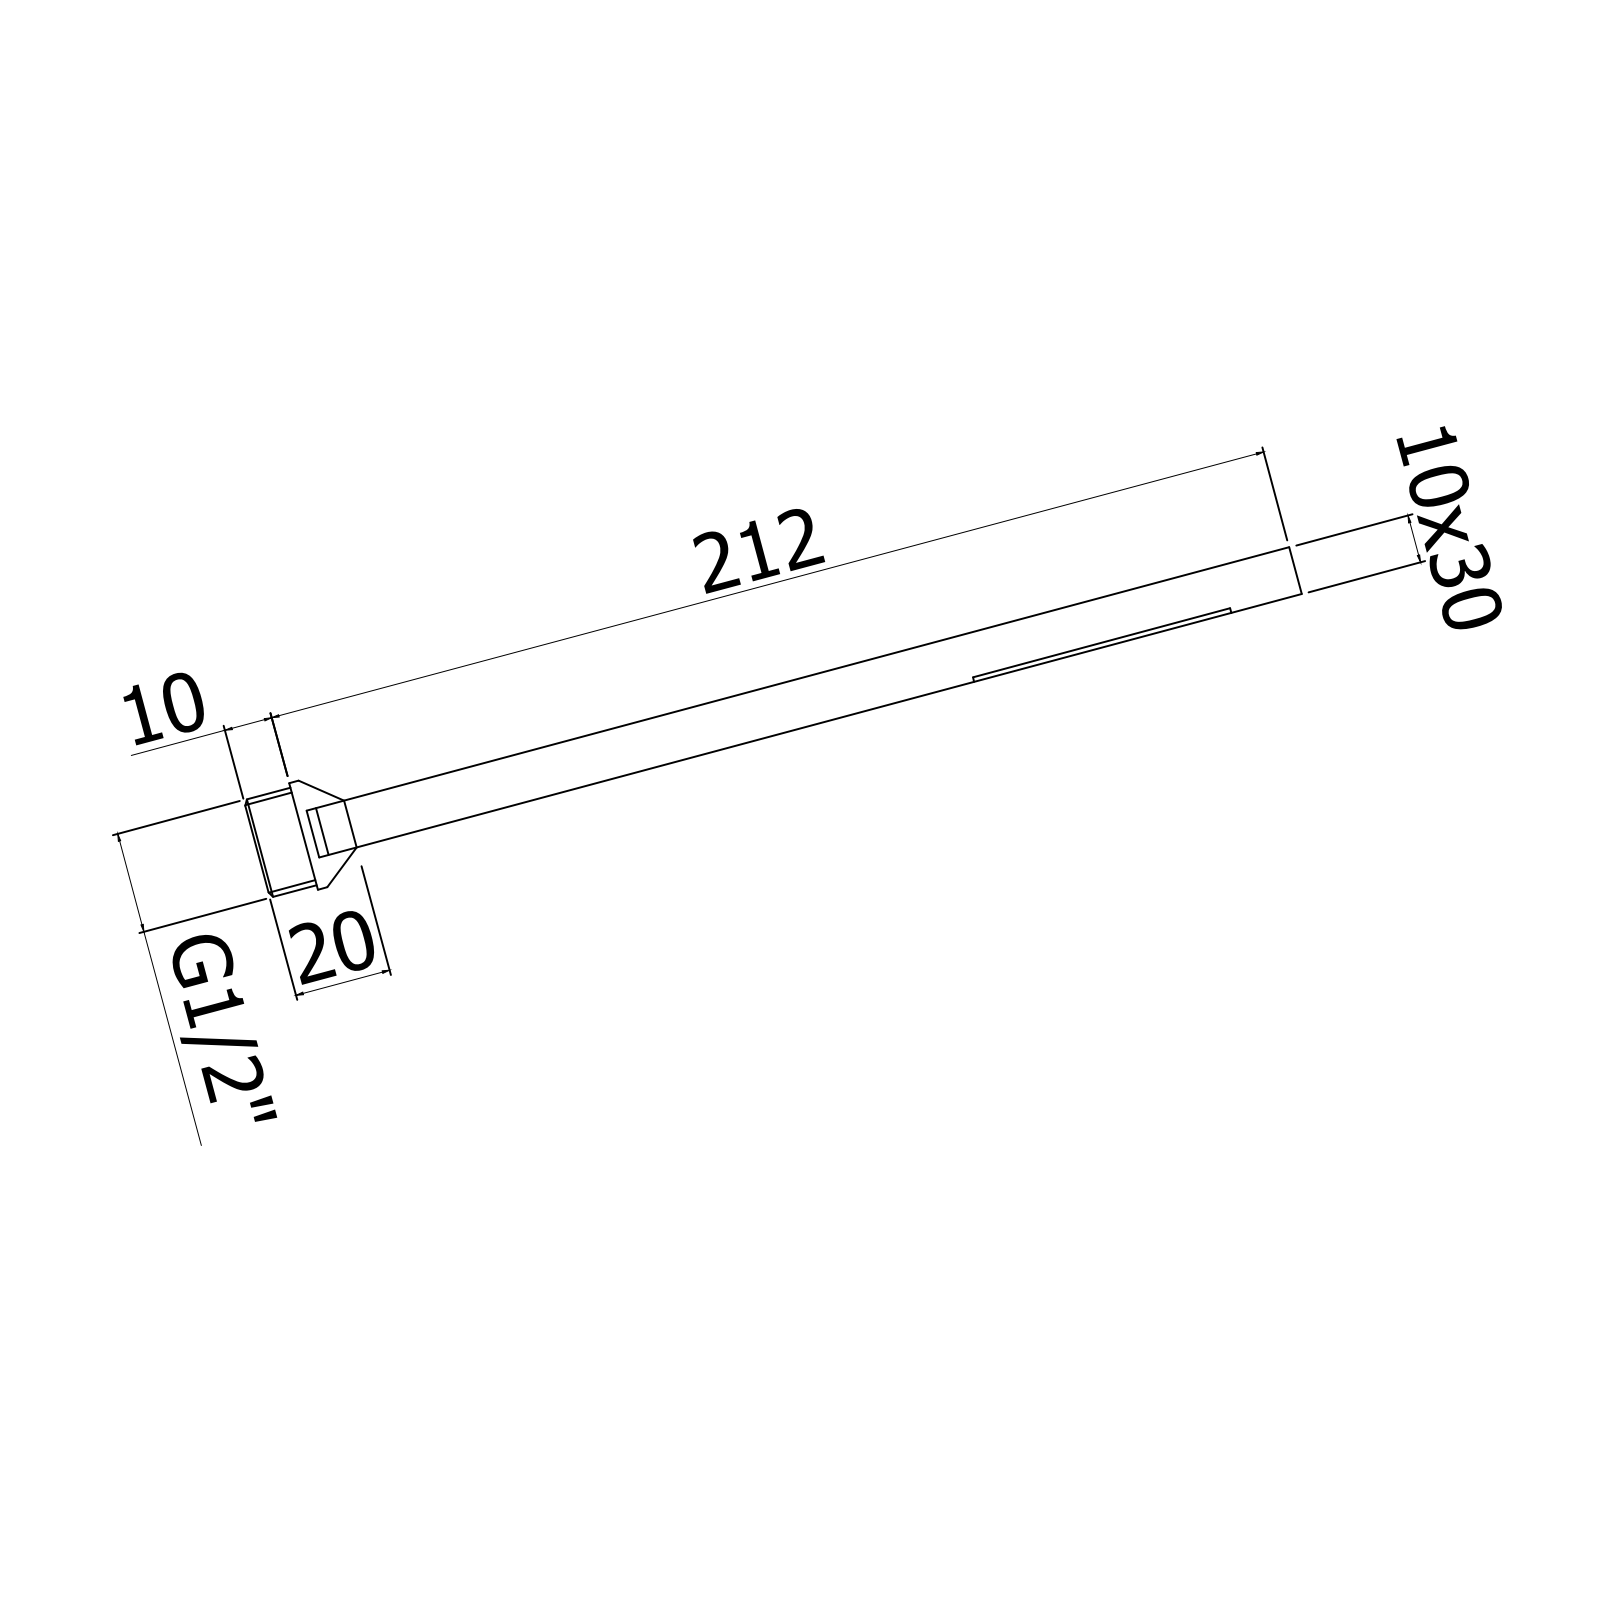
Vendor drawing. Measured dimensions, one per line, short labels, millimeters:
name: ZDOC117CR
written by: CREO PARAMETRIC BY PTC INC, 2020044 (CONFIG_CONTROL_DESIGN)
unit: mm
bodies: 0 solids, 284 faces (237 planar, 29 cylindrical, 18 other)
size: 224 × 30 × 22.5
bosses: 11× ⌀2, 1× ⌀22.5, 1× ⌀19
rounds: 2× R4, 1× R113
face distances: 10, 30, 9.8, 1, 3, 1.2, 8.8, 7, 6.8, 5.8
